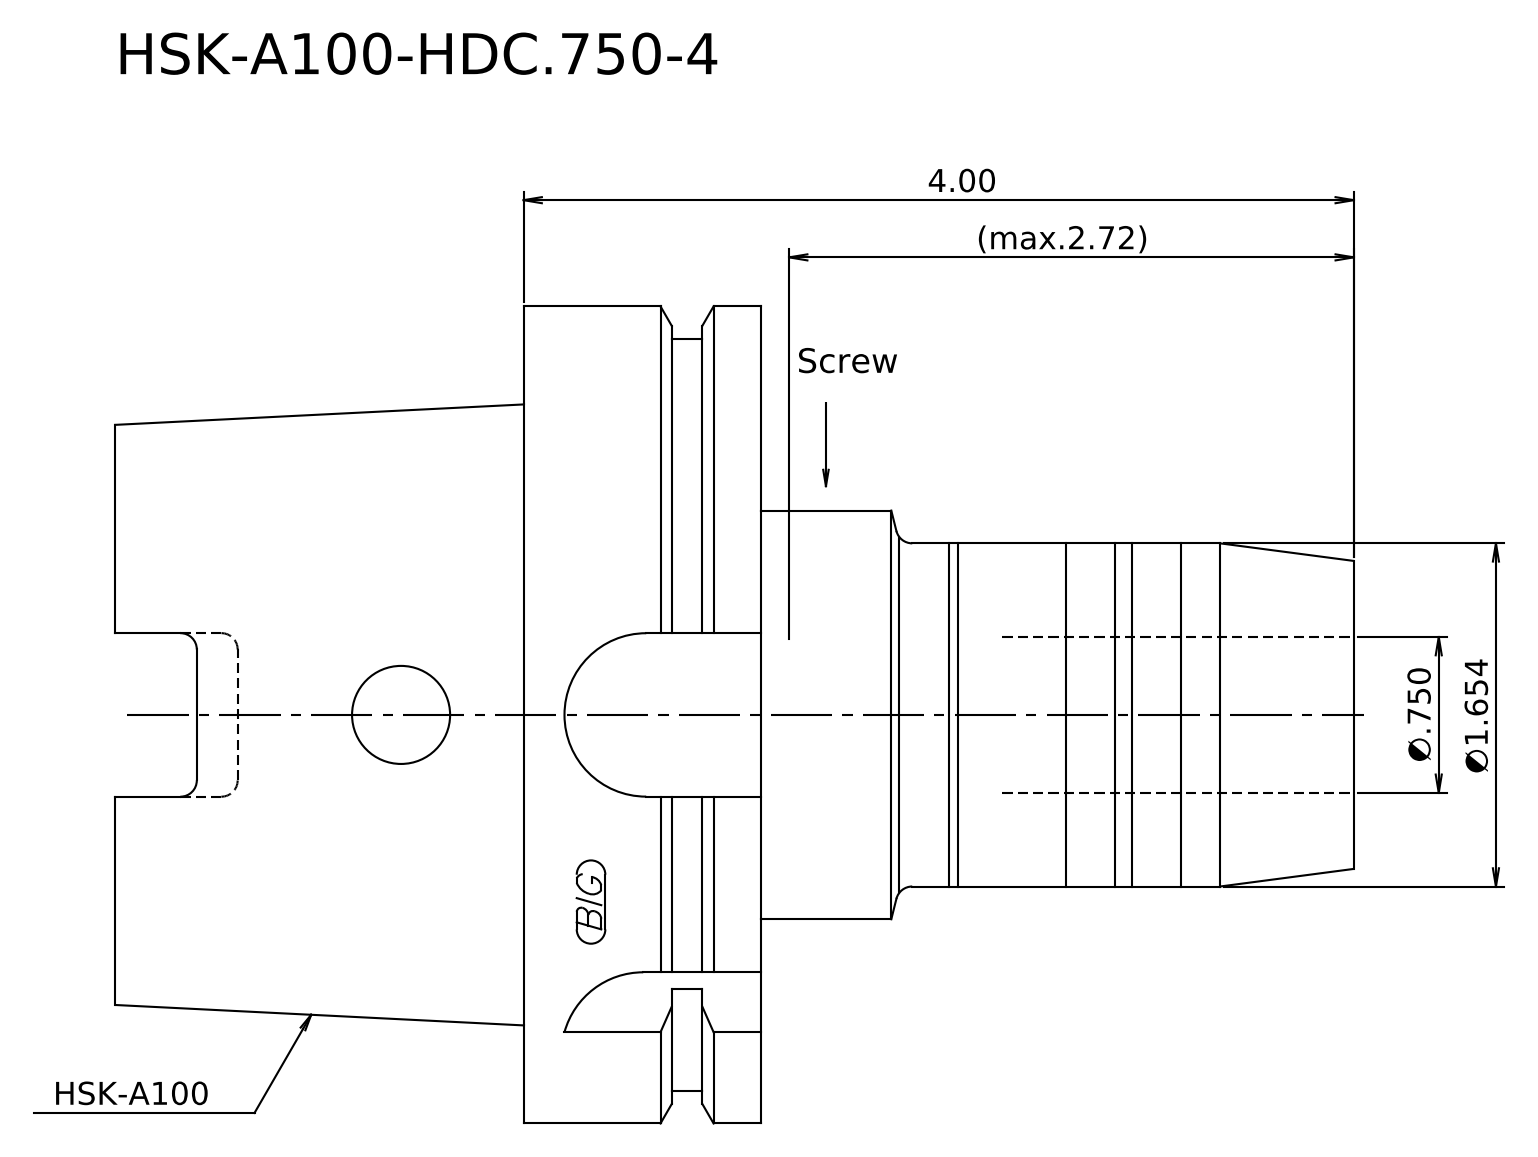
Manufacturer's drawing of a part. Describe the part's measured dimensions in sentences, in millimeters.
Its 3-D file was written by "Kubotek KeyCreator 2011 V10.0.2 (22737) (automotive_design)". It is 1 solid with 16 faces: 6 planar, 5 cylindrical and 5 other. Overall it measures 151.6 by 100 by 100 millimeters. Its volume is 542 767 cubic millimeters and its surface area 46 872 square millimeters. Round bosses or shafts: 1 of diameter 100, 1 of diameter 92, 1 of diameter 50, 1 of diameter 42. The main face-to-face distances are 79, 29, 50, 72.6, 101.6, 151.6, 79.72, 7.12, 21.88, 71.88.
